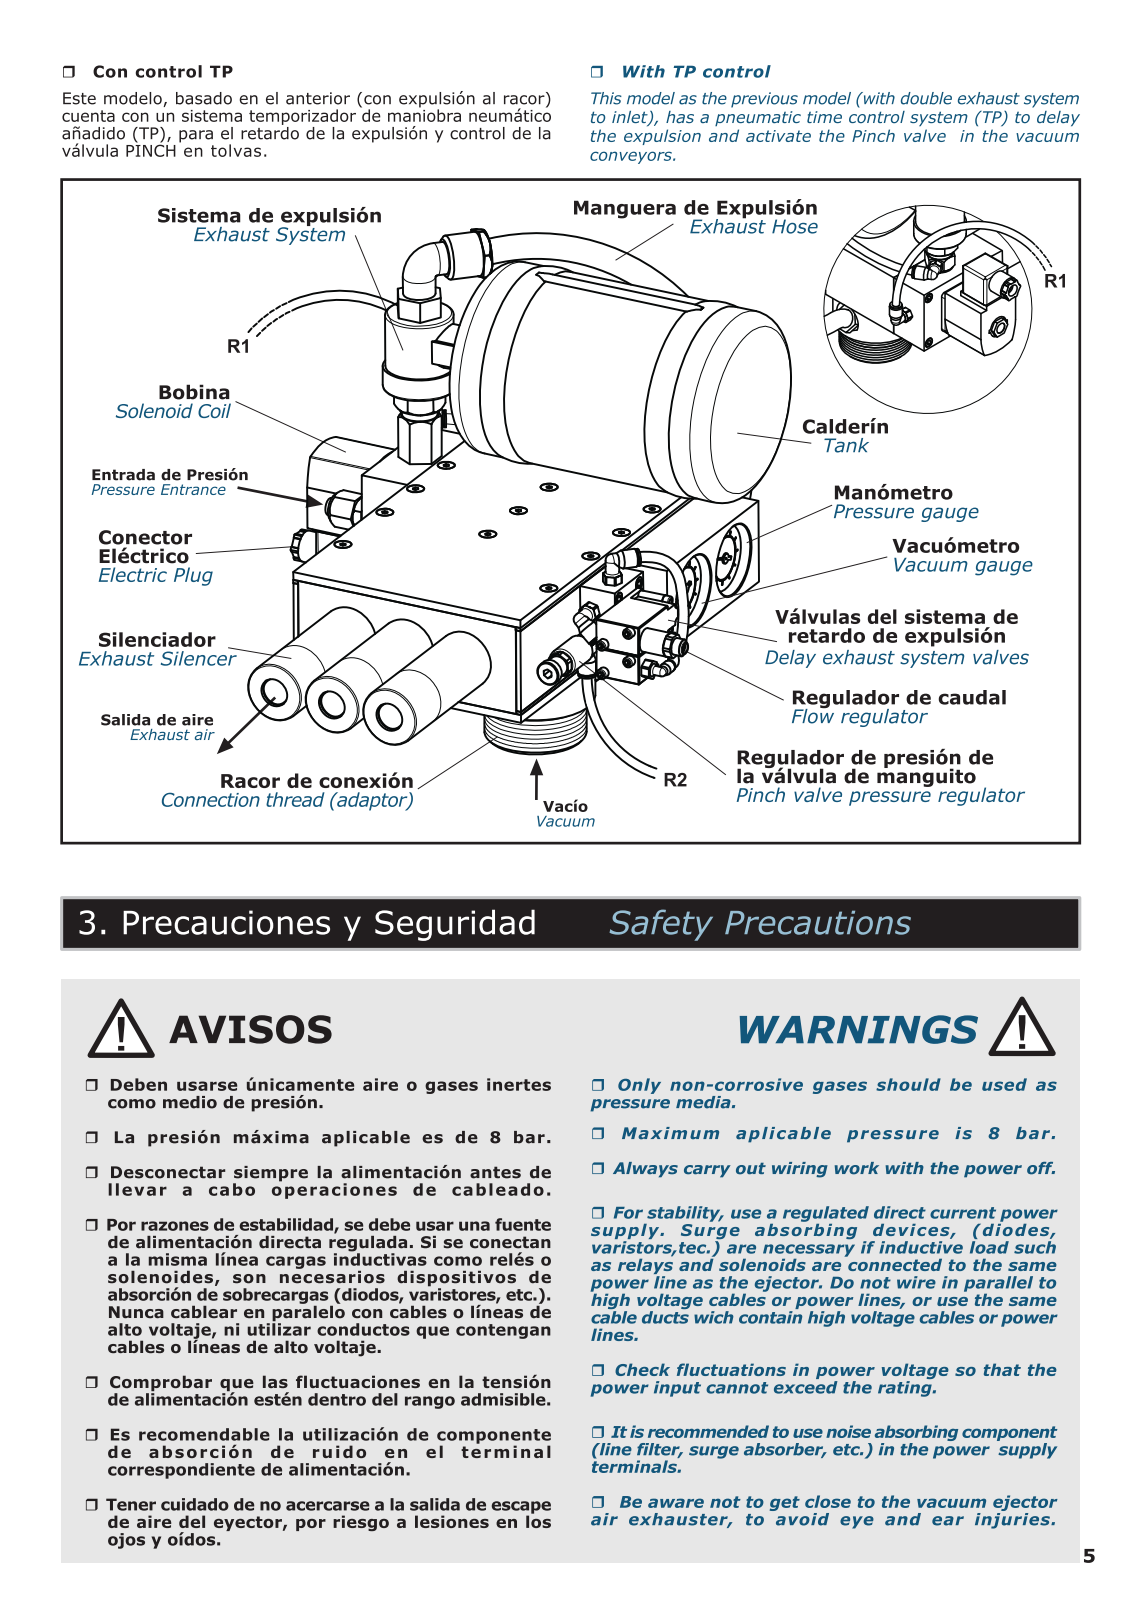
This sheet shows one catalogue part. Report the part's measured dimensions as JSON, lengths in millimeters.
{"part_name": "Pieza22", "step_written_by": "Autodesk Inventor 2019 (CONFIG_CONTROL_DESIGN)", "units": "millimeters", "bodies": {"solids": 3, "faces": 668, "planar": 438, "cylindrical": 126, "other": 104}, "overall_size": [323, 203.6, 90.1], "volume_mm3": 2716000, "surface_area_mm2": 210557, "round_holes": [[3.5, 6], [2, 3], [6.65, 3], [16, 3], [17, 3], [23, 3], [5, 2], [26.94, 2], [42.8, 2], [5.5, 1], [10.2, 1], [12, 1]], "round_bosses_or_shafts": [[35, 3], [40, 2], [25.74, 2], [22, 1], [19, 1], [18.8, 1], [14.6, 1], [13.6, 1]], "partial_cylinders_radius": [[1.75, 24], [2.5, 13], [3, 2], [5, 1], [10.5, 1]], "face_to_face_distances": [65.5, 150, 229.3, 7, 58.5, 32, 16, 35, 185, 153], "hole_center_spacings": [38, 0.93, 68.8, 1.03, 1.48, 1.75, 11.4, 17.07]}
